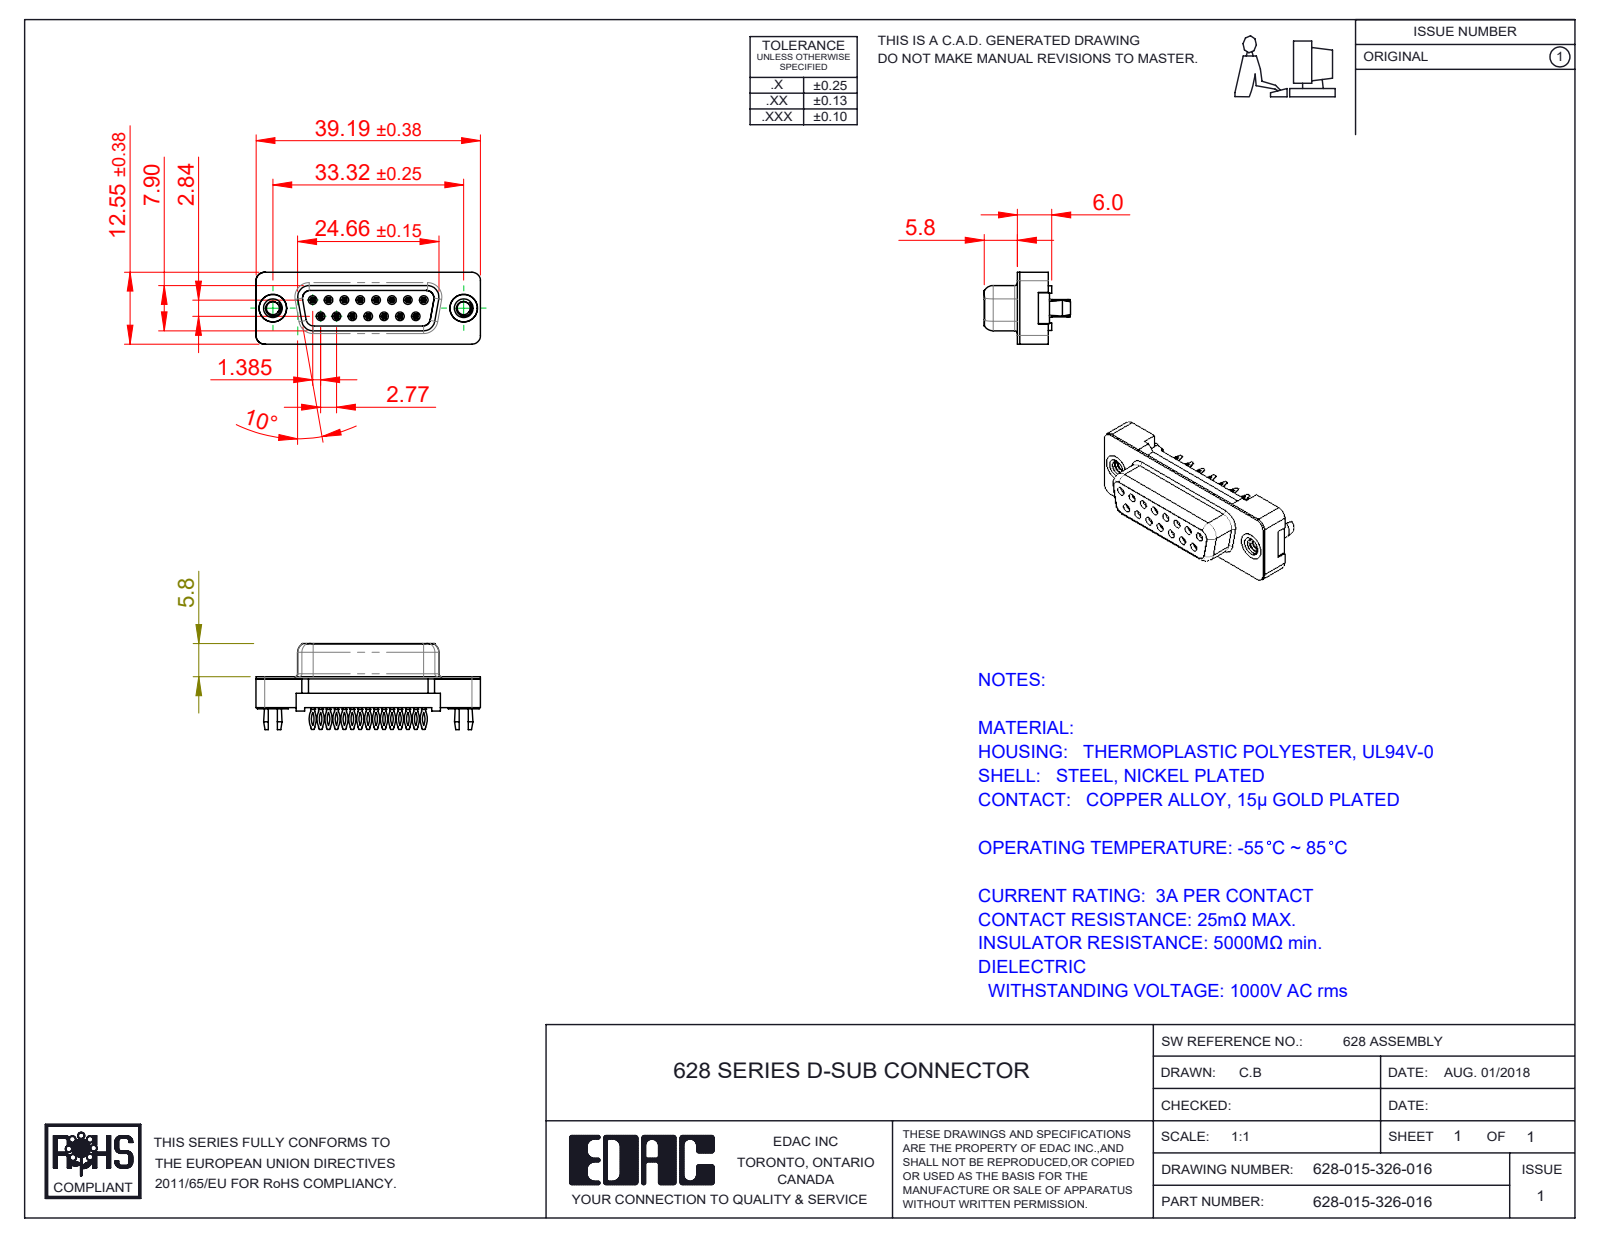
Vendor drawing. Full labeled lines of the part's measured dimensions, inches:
Part name (STEP PRODUCT): 628 PB Contact Row 1_26; 628 PB Shell_15 Contacts; 628 Plastic Body Housing_15 Contacts; 628 PB 4-40 Threaded Rivet with Boardlock (+2 more)
STEP written by: SolidWorks 2020 (CONFIG_CONTROL_DESIGN)
Units: inches
Bodies: 19 solids, 1611 faces (664 planar, 398 cylindrical, 549 other)
Overall size (bounding box): 1.543 × 0.593 × 0.494
Volume: 0.151 in³ · Surface area: 9.267 in²
Round holes (diameter × count): ⌀0.035 ×15, ⌀0.089 ×2, ⌀0.12 ×2, ⌀0.157 ×2, ⌀0.189 ×2, ⌀0.197 ×2
Round bosses / shafts (diameter × count): ⌀0.193 ×2
Partial cylindrical surfaces — rounded edges, fillets, slot ends (radius × count): R0.01 ×60, R0.115 ×30, R0.131 ×30, R0.02 ×19, R0.012 ×15, R0.053 ×12, R0.059 ×8, R0.035 ×4
Main face-to-face distances: 0.016, 0.218, 0.079, 0.098, 0.244, 0.109, 0.027, 0.217, 0.106, 0.139
Hole centre spacings: 0.124, 0.109, 0.218, 0.327, 0.436, 0.198, 0.198, 0.294
